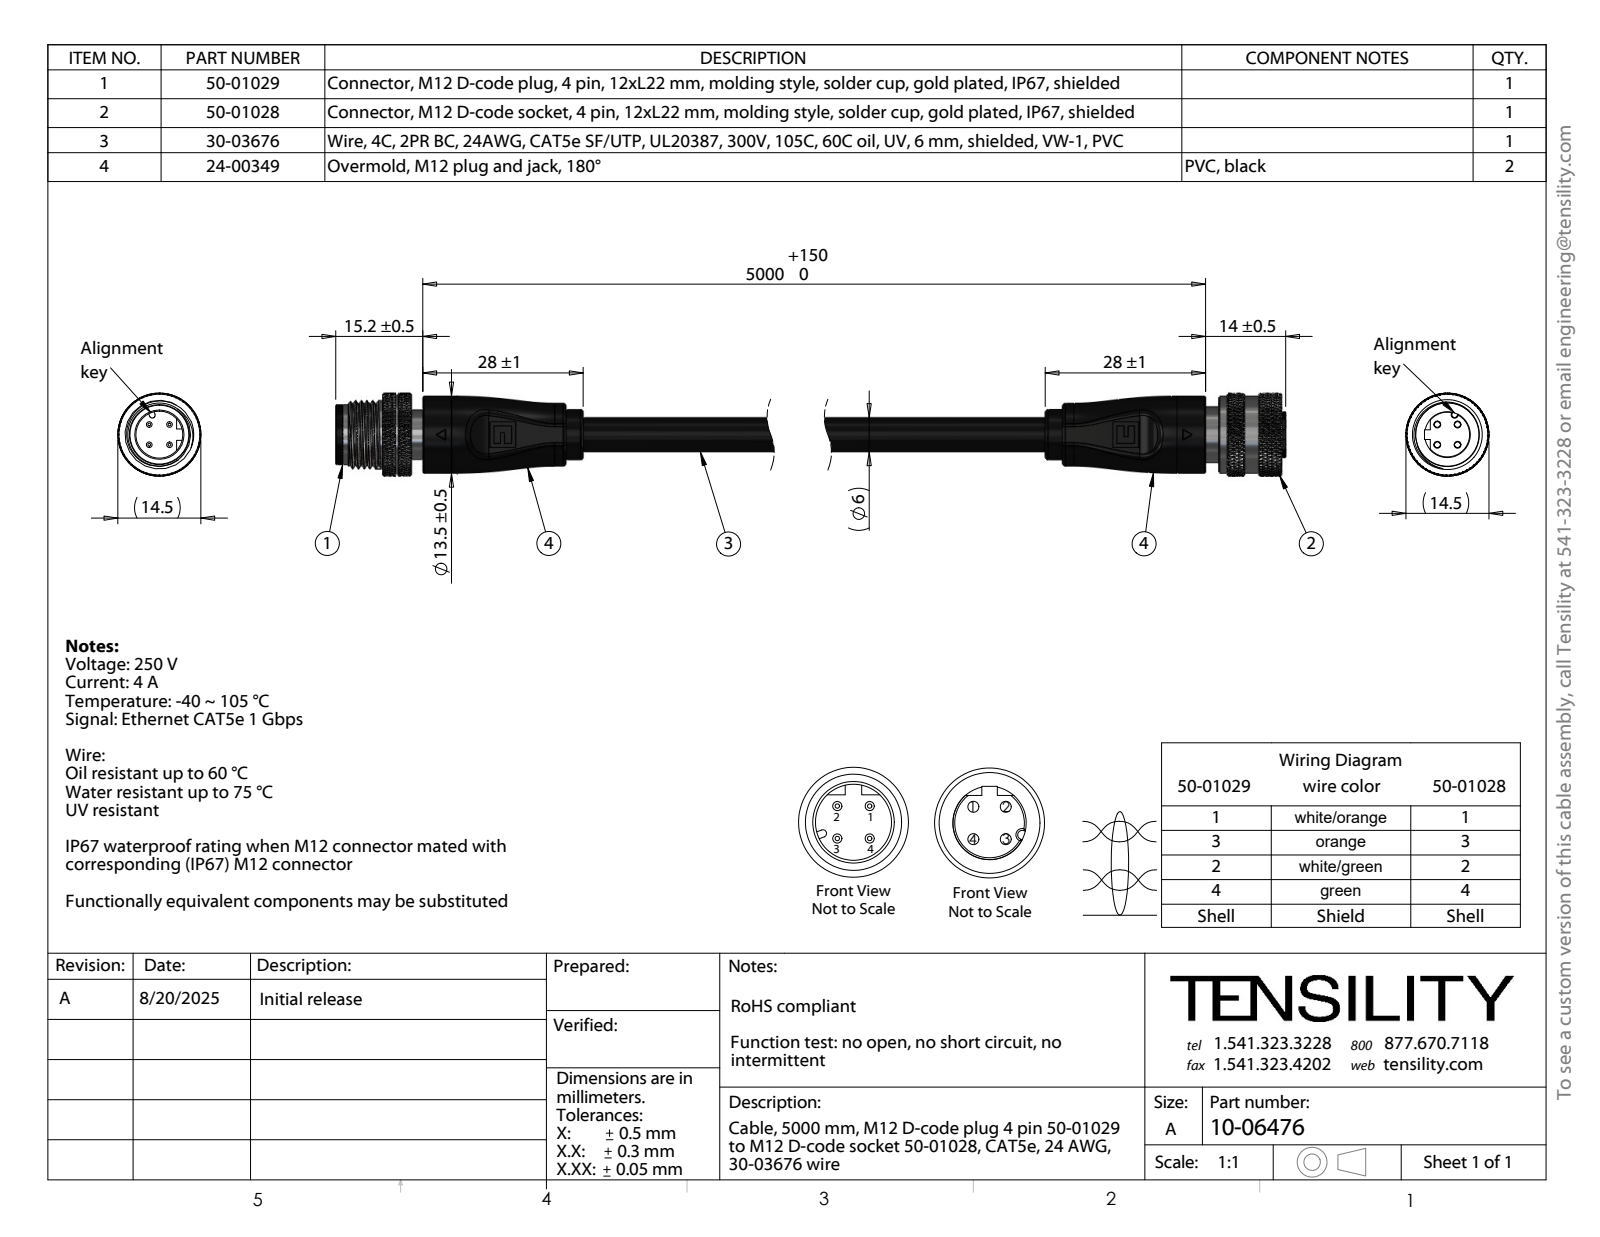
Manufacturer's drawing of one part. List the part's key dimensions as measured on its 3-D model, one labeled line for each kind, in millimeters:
Part name (STEP PRODUCT): 50-01028-04_默认; 50-01028-05_默认; 50-01029_默认; 50-01028-03_默认 (+8 more)
STEP written by: SolidWorks 2025 (CONFIG_CONTROL_DESIGN)
Units: millimetres
Bodies: 53 solids, 5792 faces (362 planar, 1477 cylindrical, 3953 other)
Overall size (bounding box): 235.2 × 14.5 × 14.5
Volume: 13 734 mm³ · Surface area: 30 639 mm²
Round holes (diameter × count): ⌀0.2 ×28, ⌀1 ×4, ⌀1.05 ×4, ⌀1.1 ×4, ⌀1.2 ×4, ⌀3.16 ×1, ⌀3.21 ×1, ⌀3.56 ×1, ⌀8.2 ×1, ⌀9.5 ×1, ⌀10 ×1, ⌀11.2 ×1
Round bosses / shafts (diameter × count): ⌀1.6 ×4, ⌀1.5 ×4, ⌀1.4 ×4, ⌀14.5 ×1, ⌀13.9 ×1, ⌀13.5 ×1, ⌀12 ×1, ⌀11 ×1
Partial cylindrical surfaces — rounded edges, fillets, slot ends (radius × count): R0.1 ×10, R0.4 ×6, R0.5 ×4, R1.5 ×2, R1.96 ×2, R5 ×2, R5.58 ×1, R6.75 ×1
Main face-to-face distances: 206, 7, 28, 178, 2, 208, 3.8, 211.8, 208.3, 5.8
Hole centre spacings: 1.91, 0.36, 2.09, 1.06, 0.89, 1.08, 1.24, 1.8
